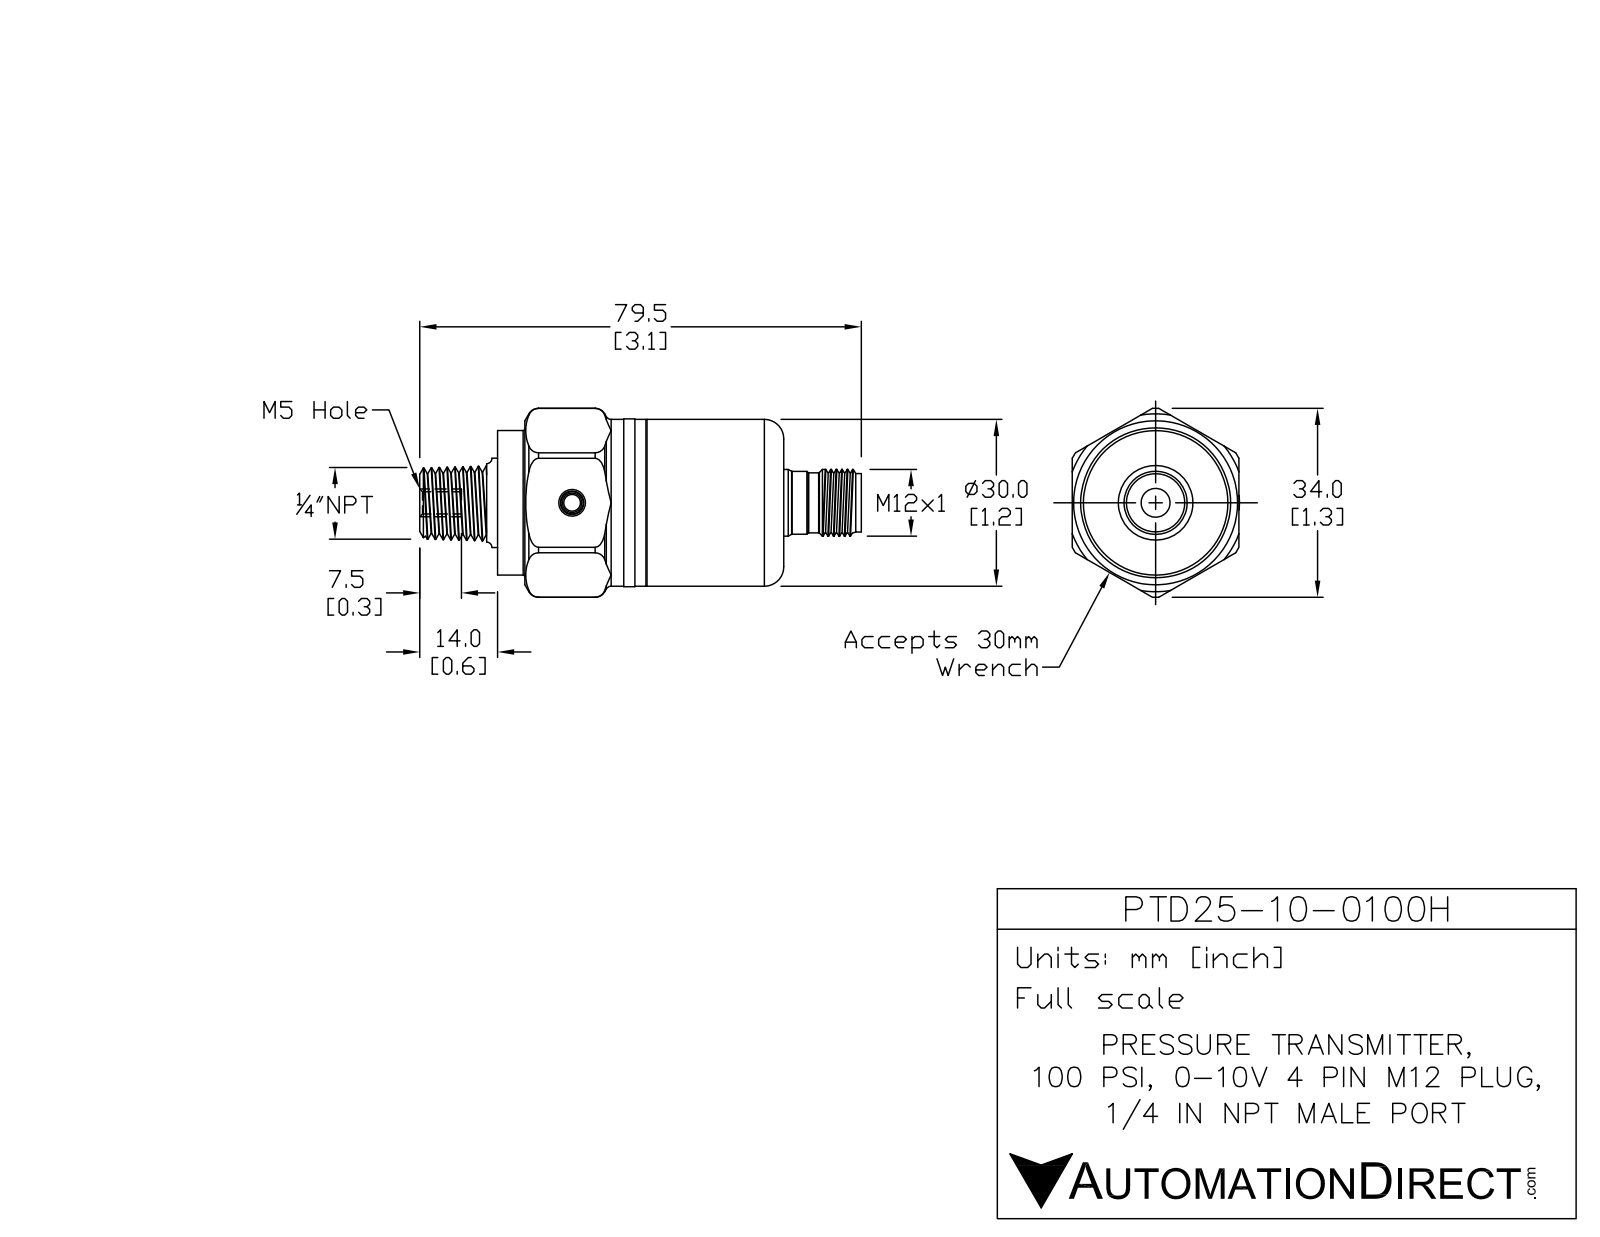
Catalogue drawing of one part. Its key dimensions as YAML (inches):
part_name: "PTD25-10-0100H"
step_written_by: "SolidWorks 2017 (AUTOMOTIVE_DESIGN)"
units: inches
bodies: {solids: 1, faces: 124, planar: 36, cylindrical: 59, other: 29}
overall_size: [3.13, 1.33, 1.248]
volume: 2.393
surface_area: 12.54
round_holes:
  - {diameter: 0.157, count: 1}
  - {diameter: 0.335, count: 1}
round_bosses_or_shafts:
  - {diameter: 1.183, count: 1}
  - {diameter: 1.181, count: 1}
  - {diameter: 1.022, count: 1}
  - {diameter: 0.551, count: 1}
  - {diameter: 0.531, count: 1}
  - {diameter: 0.472, count: 1}
partial_cylinders:
  - {radius: 0.148, count: 1}
  - {radius: 0.667, count: 1}
face_to_face_distances: [2.008, 1.18, 1.181, 1.89, 0.118, 2.559, 0.669, 0.551, 1.181, 0.222]
